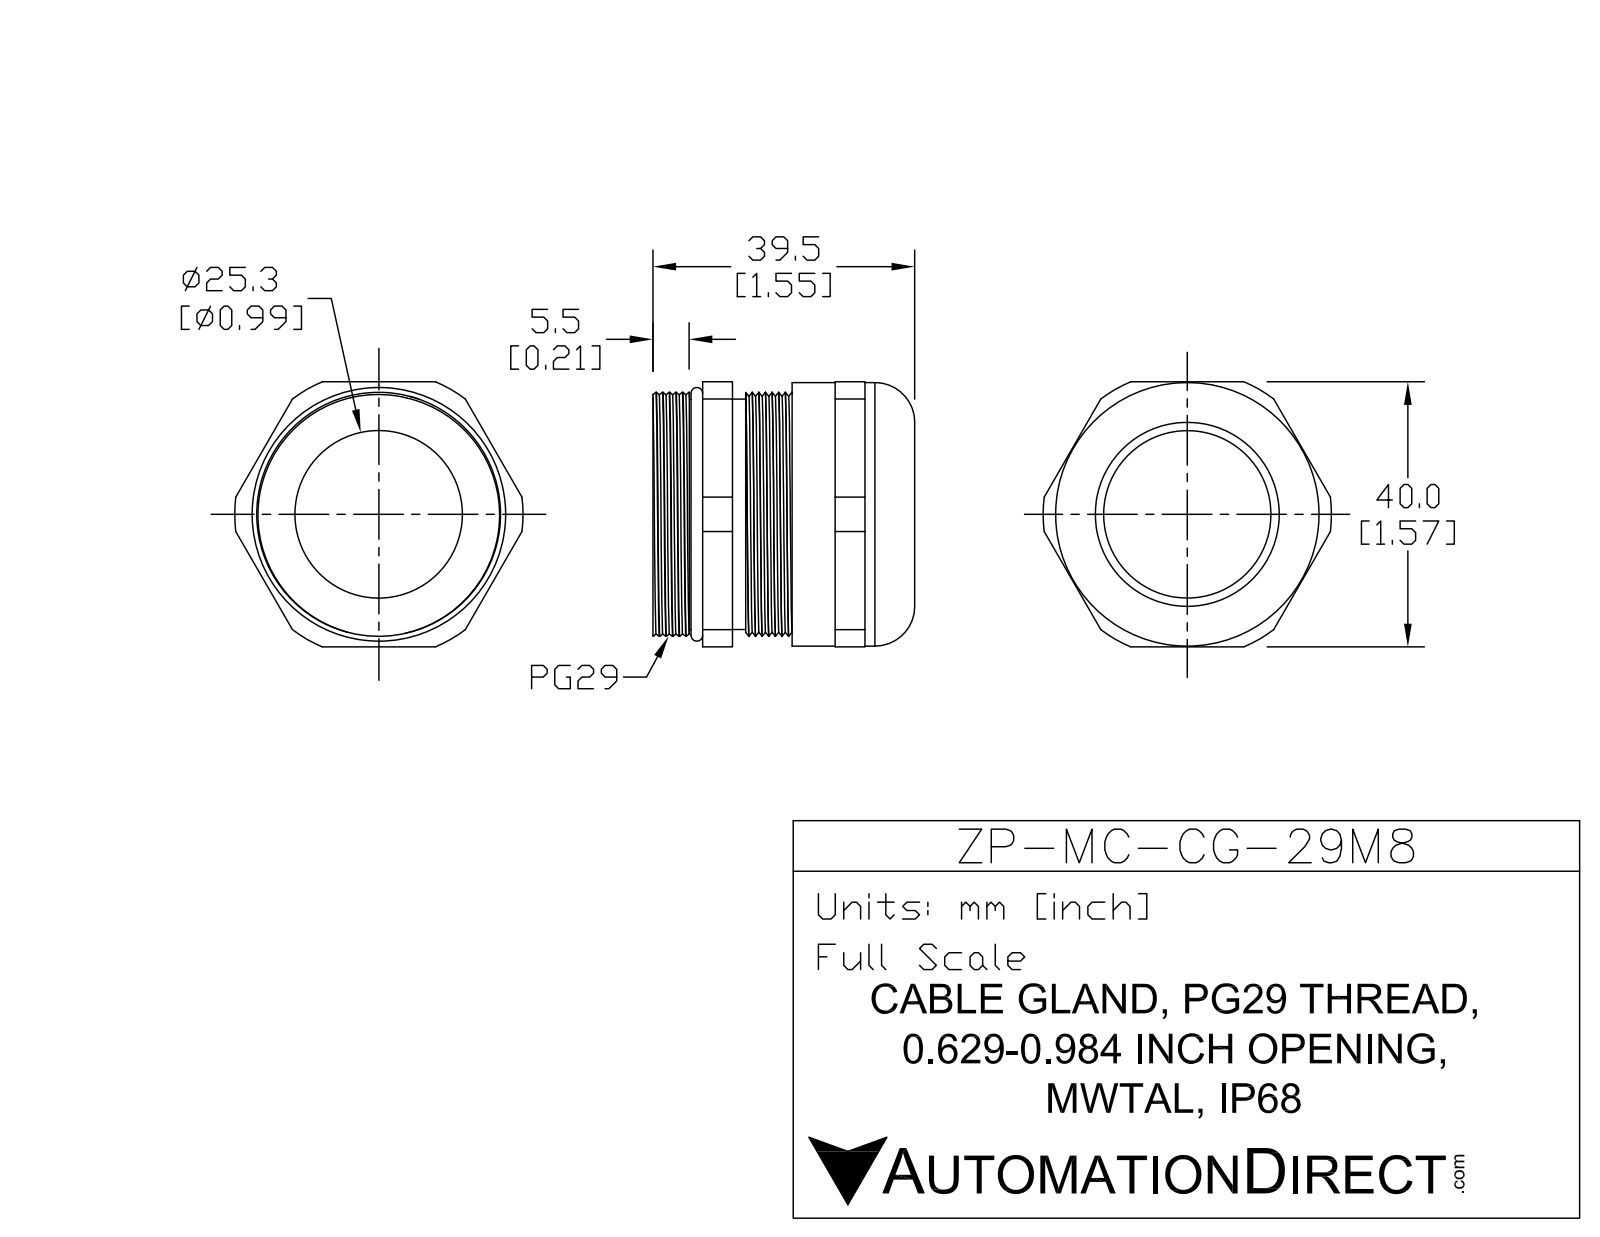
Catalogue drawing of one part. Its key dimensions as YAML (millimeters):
part_name: "ZP-MC-CG-29M8"
step_written_by: "SolidWorks 2011 (AUTOMOTIVE_DESIGN)"
units: millimeters
bodies: {solids: 2, faces: 52, planar: 23, cylindrical: 22, other: 7}
overall_size: [43.5, 40, 39.5]
volume: 25969
surface_area: 11997
round_holes:
  - {diameter: 25.25, count: 1}
  - {diameter: 37.27, count: 1}
round_bosses_or_shafts:
  - {diameter: 39.75, count: 1}
  - {diameter: 36.8, count: 1}
  - {diameter: 34.75, count: 1}
partial_cylinders:
  - {radius: 21.75, count: 1}
face_to_face_distances: [4.5, 12, 7.5, 40, 6.5, 20, 13.5, 27.5, 32, 15.5]
